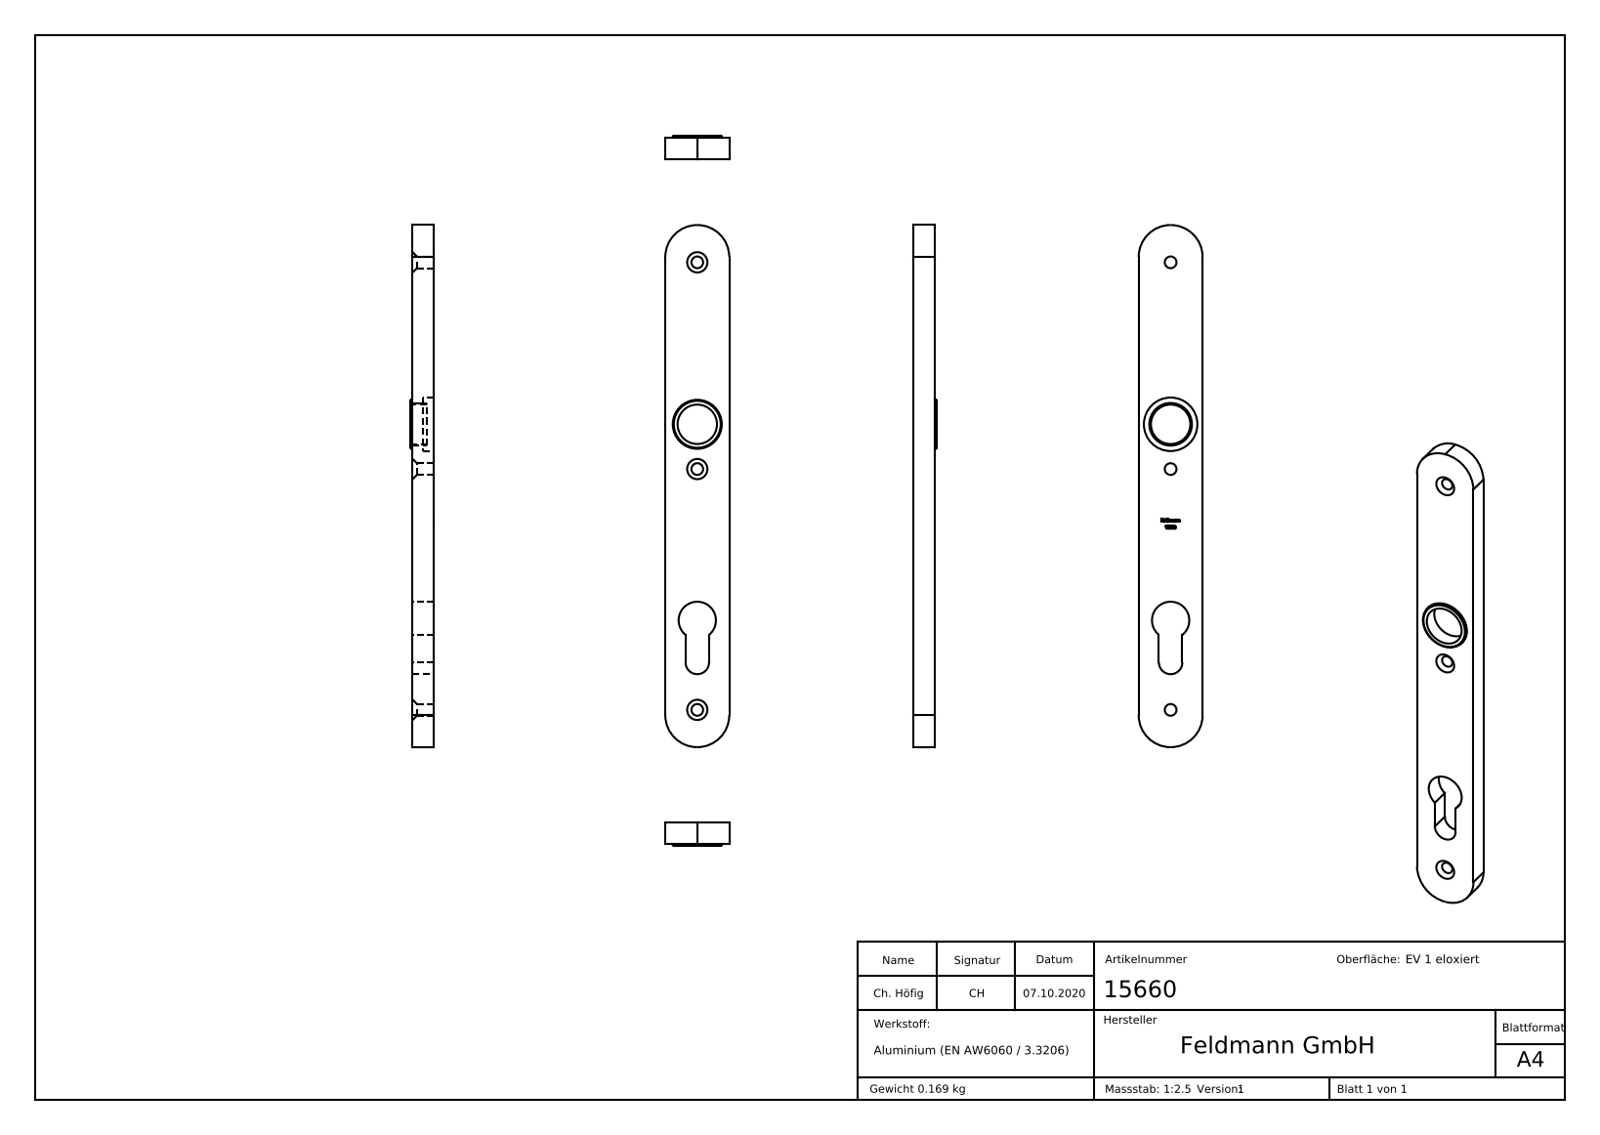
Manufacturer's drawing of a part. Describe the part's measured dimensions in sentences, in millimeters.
The part is named "AMF Schliessblech Konfig Teil2_15552 Teil2; AMF Schliessblech Konfig Teil1_15660 Teil1; AMF Schliessblech Konfig Teil1; AMF Schliessblech Konfig Teil2 (+1 more)". Its 3-D file was written by "SolidWorks 2018 (CONFIG_CONTROL_DESIGN)". It is 2 solids with 216 faces: 101 planar, 24 cylindrical and 91 other. Overall it measures 245 by 30 by 11 millimeters. Its volume is 62 961 cubic millimeters and its surface area 21 200 square millimeters. Round holes: 3 of diameter 5.5, 1 of diameter 18.5, 1 of diameter 20, 1 of diameter 25.1. Round bosses or shafts: 1 of diameter 23. Partial cylindrical surfaces (rounded edges, fillets, slot ends): 2 of radius 15, 1 of radius 5.5, 1 of radius 8.75. The main face-to-face distances are 10, 30, 5, 9.5, 20.5, 11, 6, 1, 3.5, 1.5. The hole center spacings are 21, 76, 97, 113, 134, 210.
